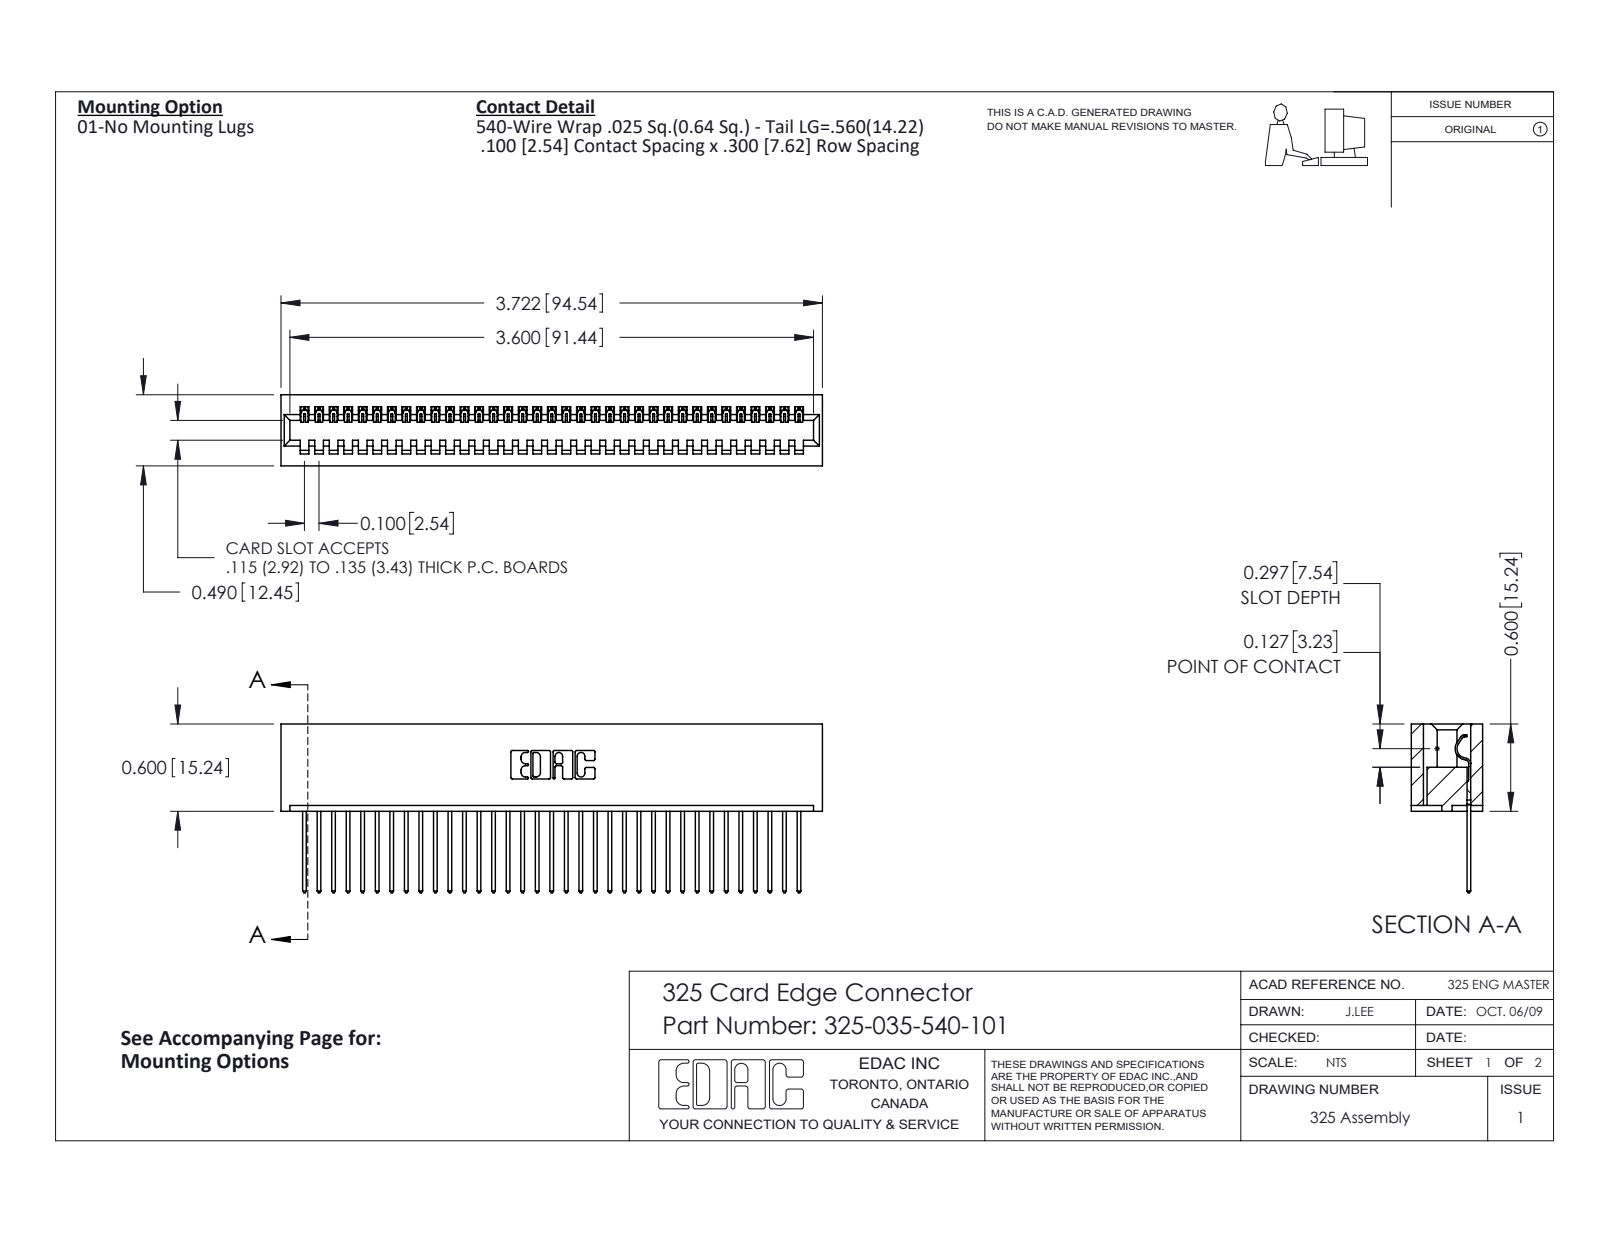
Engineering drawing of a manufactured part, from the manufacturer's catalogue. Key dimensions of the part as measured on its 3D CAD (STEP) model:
Part name (STEP PRODUCT): 325-035-540-101; 325 Part_Lugless; 325-292-001_325-293-140
STEP written by: SolidWorks 2016 (CONFIG_CONTROL_DESIGN)
Units: inches
Bodies: 36 solids, 2136 faces (1536 planar, 600 cylindrical, 0 other)
Overall size (bounding box): 3.722 × 1.16 × 0.49
Volume: 0.767 in³ · Surface area: 22.4 in²
Partial cylindrical surfaces — rounded edges, fillets, slot ends (radius × count): R0.006 ×70, R0.01 ×70, R0.01 ×22, R0.007 ×6, R0.031 ×6, R0.026 ×3, R0.014 ×1, R0.022 ×1
Main face-to-face distances: 0.083, 0.407, 0.3, 0.49, 0.107, 0.383, 0.025, 0.325, 0.56, 0.263
